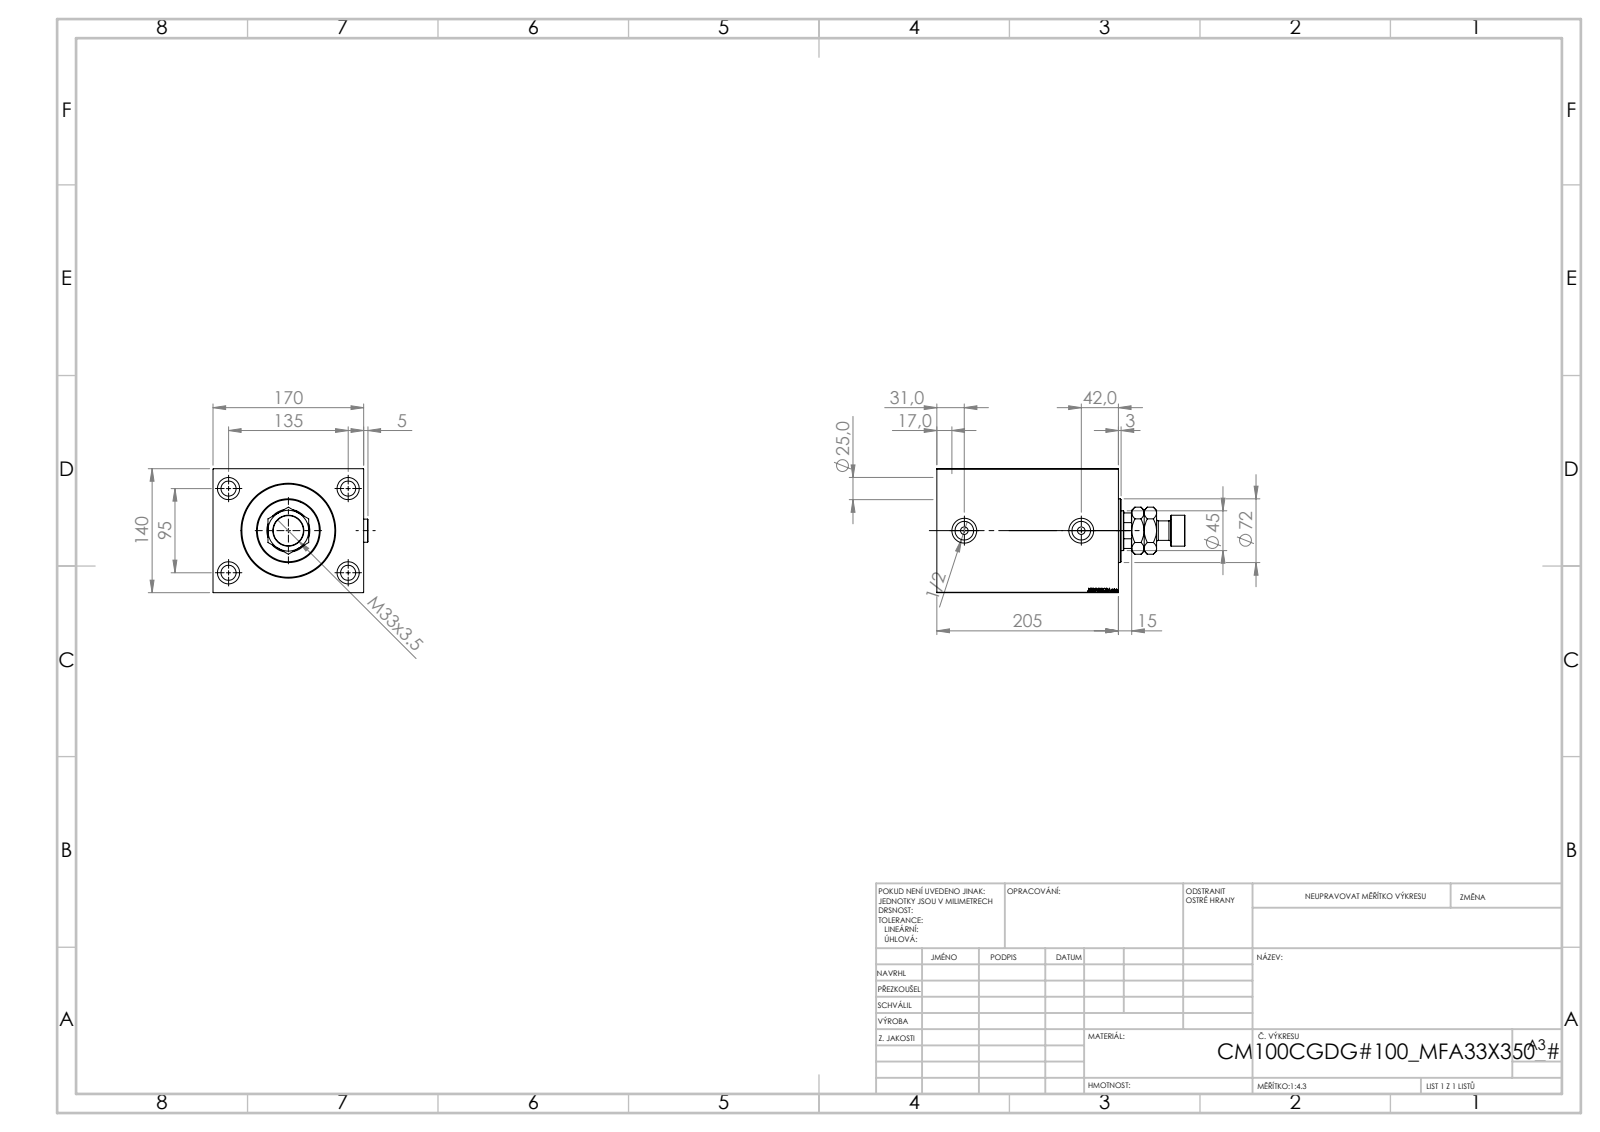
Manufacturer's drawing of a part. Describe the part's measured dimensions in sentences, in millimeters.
The part is named "V450CM_C_VCP; V450CM_VC_B; MFA; Zatka_OIL_PORT (+1 more)". Its 3-D file was written by "SolidWorks 2019 (CONFIG_CONTROL_DESIGN)". It is 6 solids with 971 faces: 459 planar, 82 cylindrical and 430 other. Overall it measures 280 by 174.9 by 140 millimeters. Its volume is 4 081 000 cubic millimeters and its surface area 376 486 square millimeters. Round holes: 4 of diameter 17, 4 of diameter 25, 2 of diameter 8.5, 2 of diameter 20.96, 2 of diameter 28, 1 of diameter 31.5, 1 of diameter 45, 1 of diameter 48.5, 1 of diameter 100, 1 of diameter 102, 1 of diameter 105. Round bosses or shafts: 2 of diameter 26, 1 of diameter 72, 1 of diameter 35, 1 of diameter 22. Partial cylindrical surfaces (rounded edges, fillets, slot ends): 1 of radius 22. The main face-to-face distances are 140, 170, 205, 179, 26, 15, 190, 90, 164, 64. The hole center spacings are 82.54, 95, 135, 165.08, 132.
